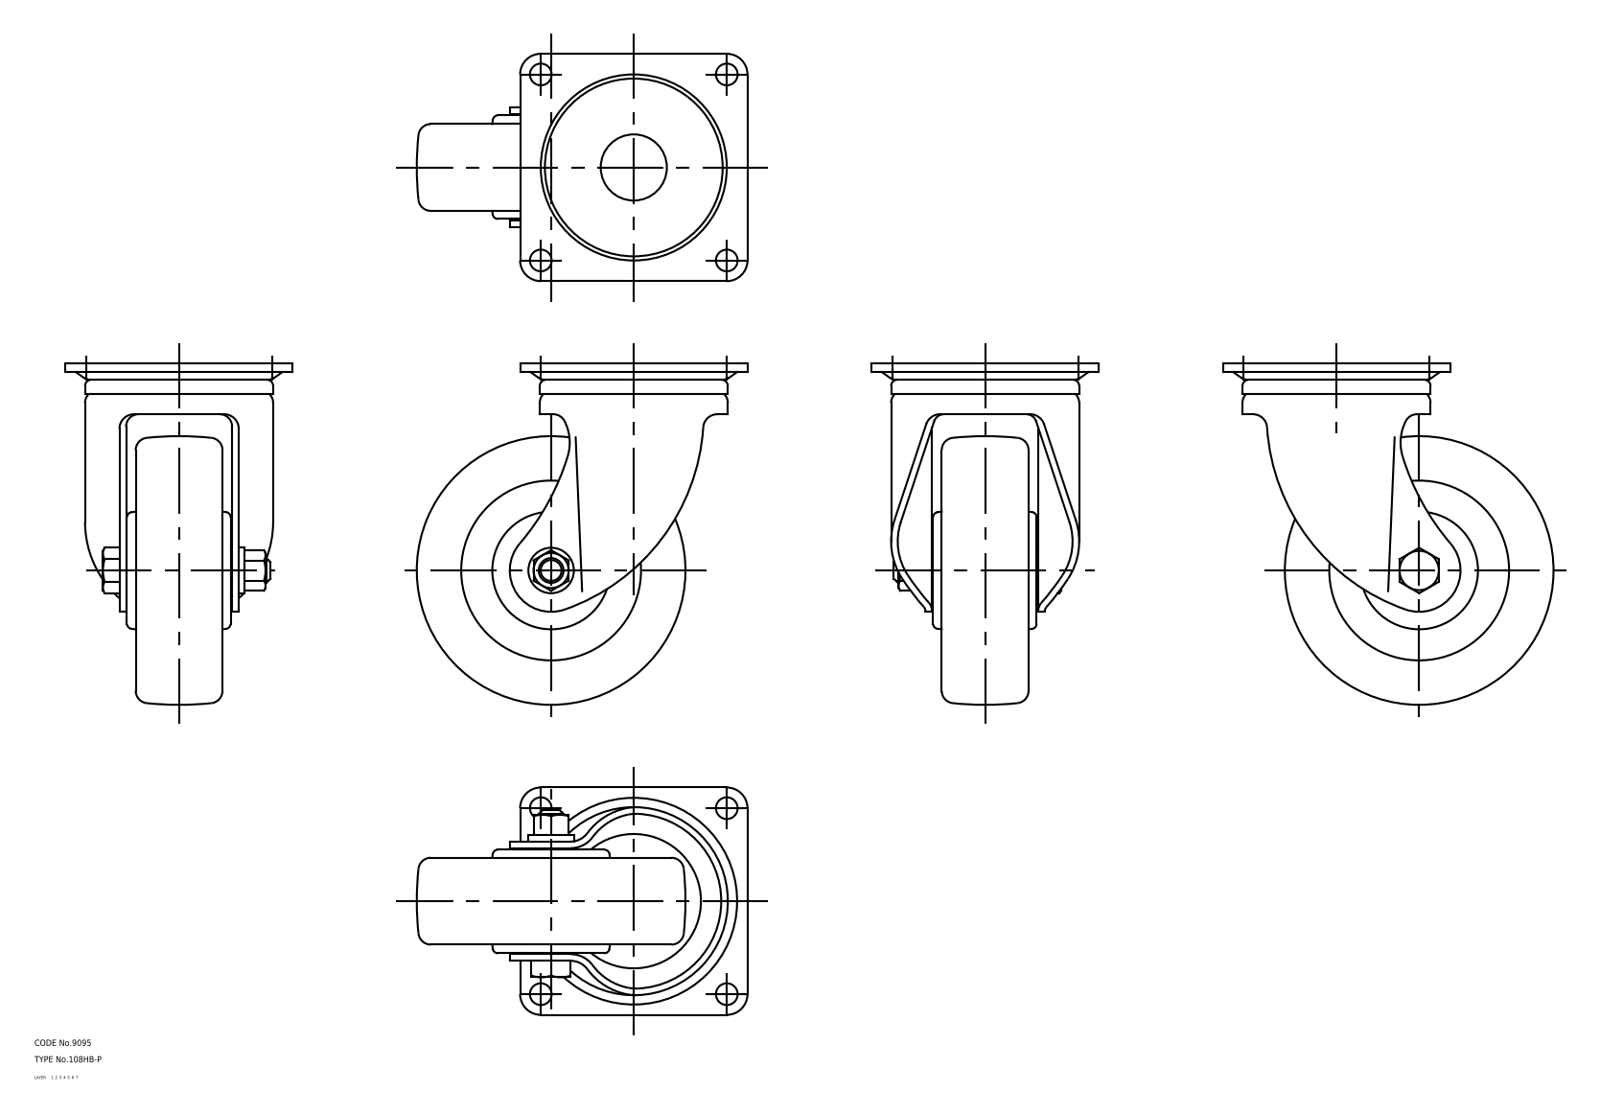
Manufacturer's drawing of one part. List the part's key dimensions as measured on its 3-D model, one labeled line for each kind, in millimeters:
Part name (STEP PRODUCT): 67126633; 67126646; 67126659; 67126672 (+1 more)
STEP written by: CADfix (AUTOMOTIVE_DESIGN)
Units: millimetres
Bodies: 5 solids, 243 faces (0 planar, 0 cylindrical, 243 other)
Overall size (bounding box): 165 × 160 × 110
Volume: 702 328 mm³ · Surface area: 130 382 mm²
